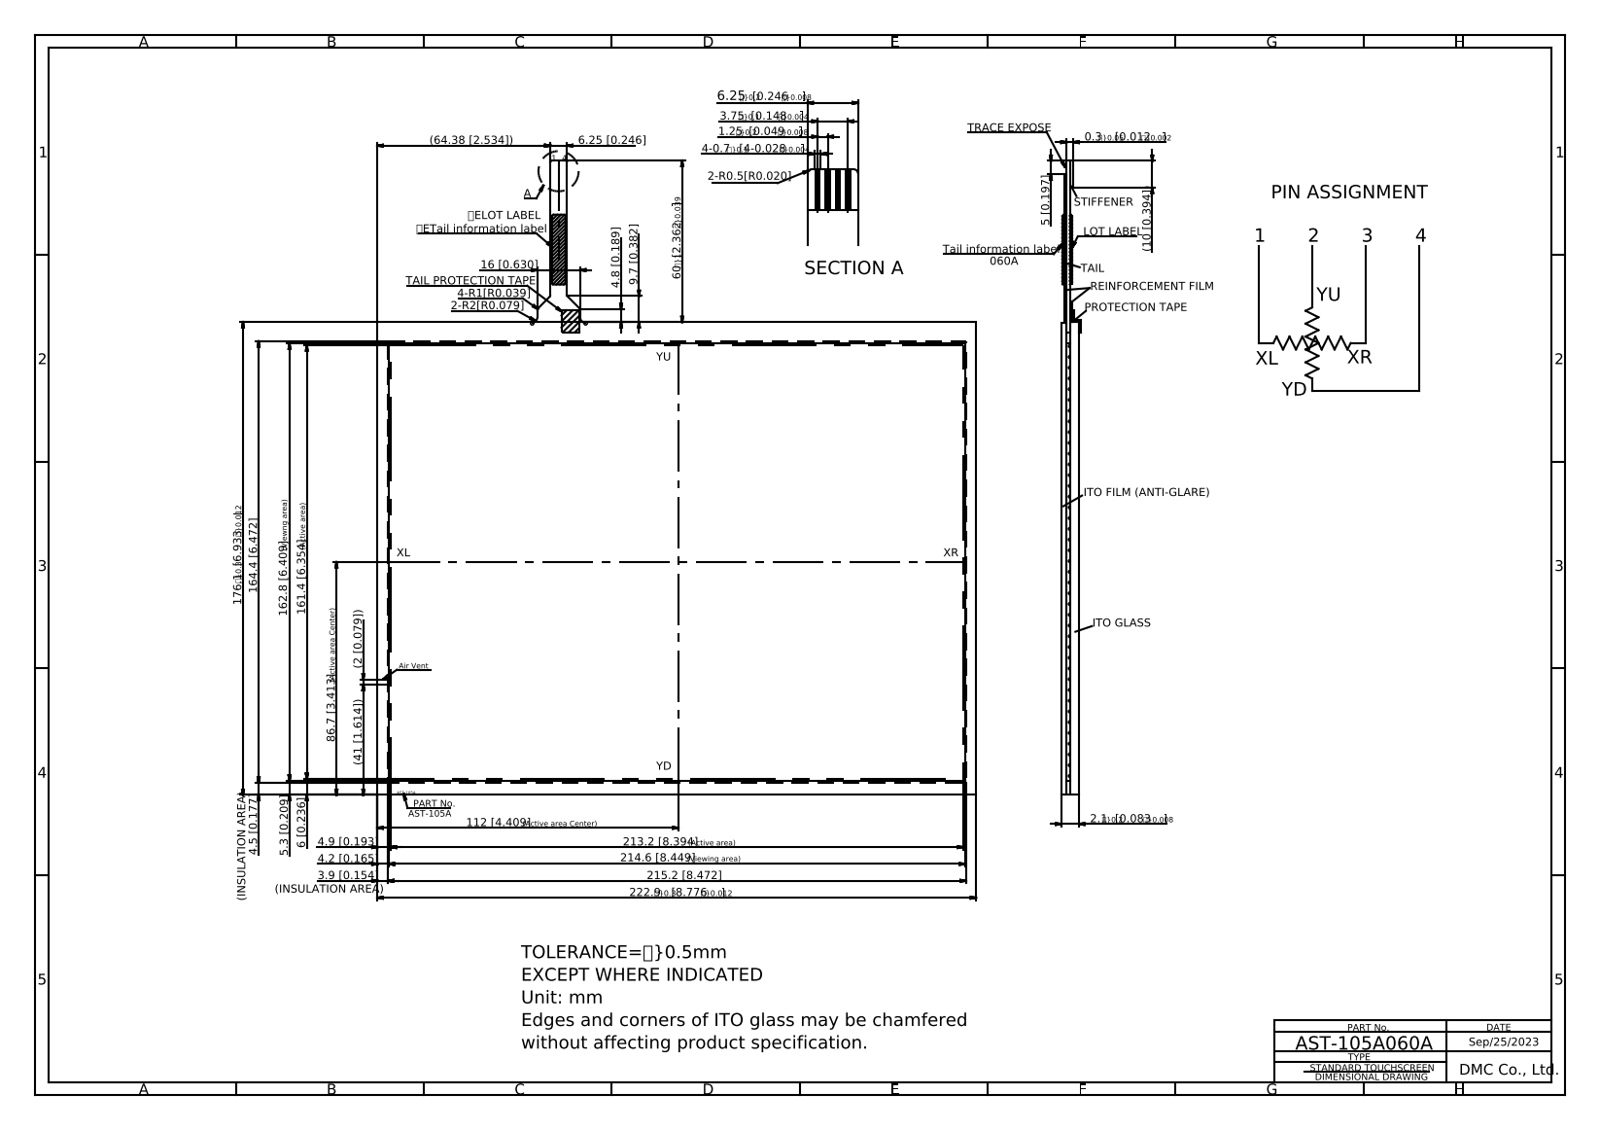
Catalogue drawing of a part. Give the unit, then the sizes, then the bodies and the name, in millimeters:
Units: millimetres
Overall size (bounding box): 312.06 × 271.32 × 1.35
Partial cylindrical surfaces — rounded edges, fillets, slot ends (radius × count): R1 ×4, R0.5 ×2
Main face-to-face distances: 1.35, 1.25, 1.15, 1.05, 176.1, 222.9, 0.7, 0.75, 0.4, 0.5
Volume: 52 998 mm³ · Surface area: 80 639 mm²
Bodies: 1 solid, 51 faces (45 planar, 6 cylindrical, 0 other)
Part name (STEP PRODUCT): AST-105A060A
STEP written by: Autodesk Inventor 2020 (CONFIG_CONTROL_DESIGN)
